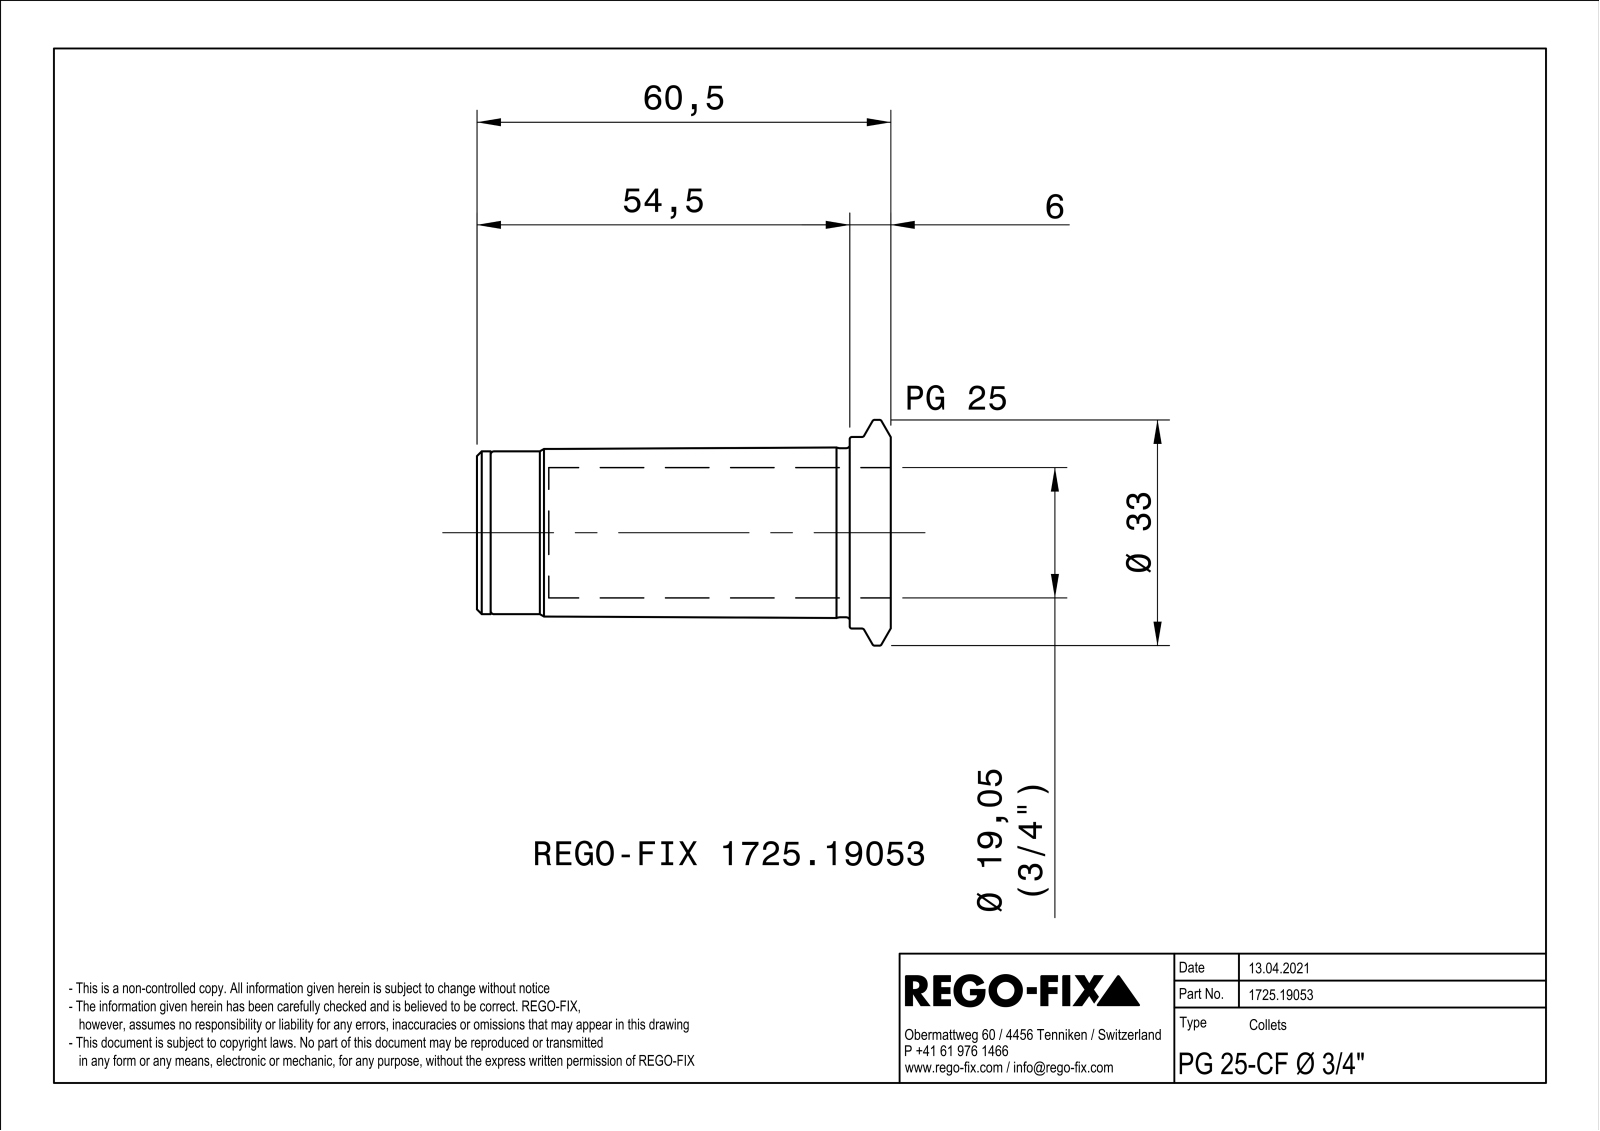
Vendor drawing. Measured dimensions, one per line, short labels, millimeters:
name: NOCUT
written by: SIEMENS PLM Software Solid Edge ST10 (AUTOMOTIVE_DESIGN)
unit: mm
bodies: 1 solid, 89 faces (23 planar, 27 cylindrical, 39 other)
size: 60.5 × 33 × 32.99
volume: 14 061 mm³; area: 11 174 mm²
holes: 3× ⌀2.5, 1× ⌀5.2, 1× ⌀6.92, 1× ⌀8.2, 1× ⌀19.05, 1× ⌀20.92, 1× ⌀22.2
bosses: 1× ⌀33, 1× ⌀28, 1× ⌀24.7, 1× ⌀23.8, 1× ⌀20.4, 1× ⌀12
rounds: 3× R0.75
face distances: 1, 60.5, 52.6, 7.9, 58.5, 5.9, 2, 50, 2.6, 8.5
hole spacings: 7.75, 13.43, 13.42
